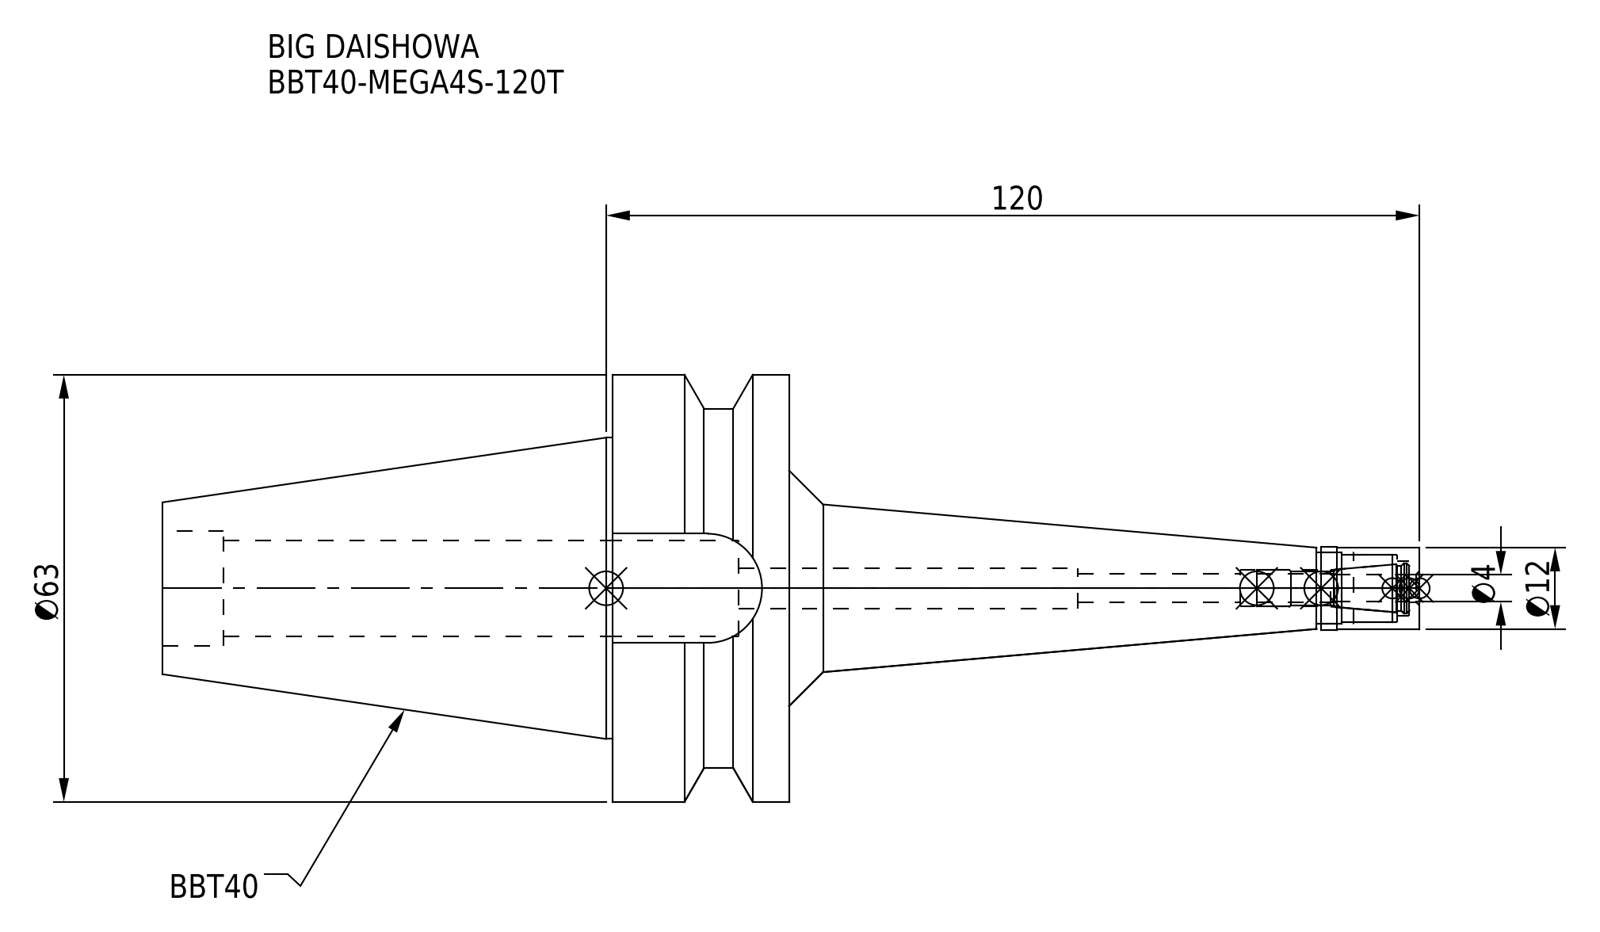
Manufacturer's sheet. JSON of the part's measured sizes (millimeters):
{"part_name": "BBT40-MEGA4S-120T-040-FreeParts; MGN4S_1.stp; BBT40-MEGA4S-120T_1.stp; DXF_TEMP_ASSY_ASM_4_ASM.stp (+3 more)", "step_written_by": "SolidWorks 2019 (CONFIG_CONTROL_DESIGN)", "units": "millimeters", "bodies": {"solids": 2, "faces": 74, "planar": 22, "cylindrical": 38, "other": 14}, "overall_size": [185.4, 63, 63], "volume_mm3": 144276, "surface_area_mm2": 29884, "round_holes": [[4.1, 1], [4.2, 1], [5.4, 1], [6, 1], [8, 1], [10, 1], [10.5, 1], [14.2, 1], [17, 1]], "round_bosses_or_shafts": [[63, 1], [53, 1], [44.45, 1], [12.3, 1], [12, 1]], "partial_cylinders_radius": [[8.05, 1]], "face_to_face_distances": [26, 45, 92.4, 66.4, 16.1, 7.4, 18.6, 85, 93, 100.4]}
